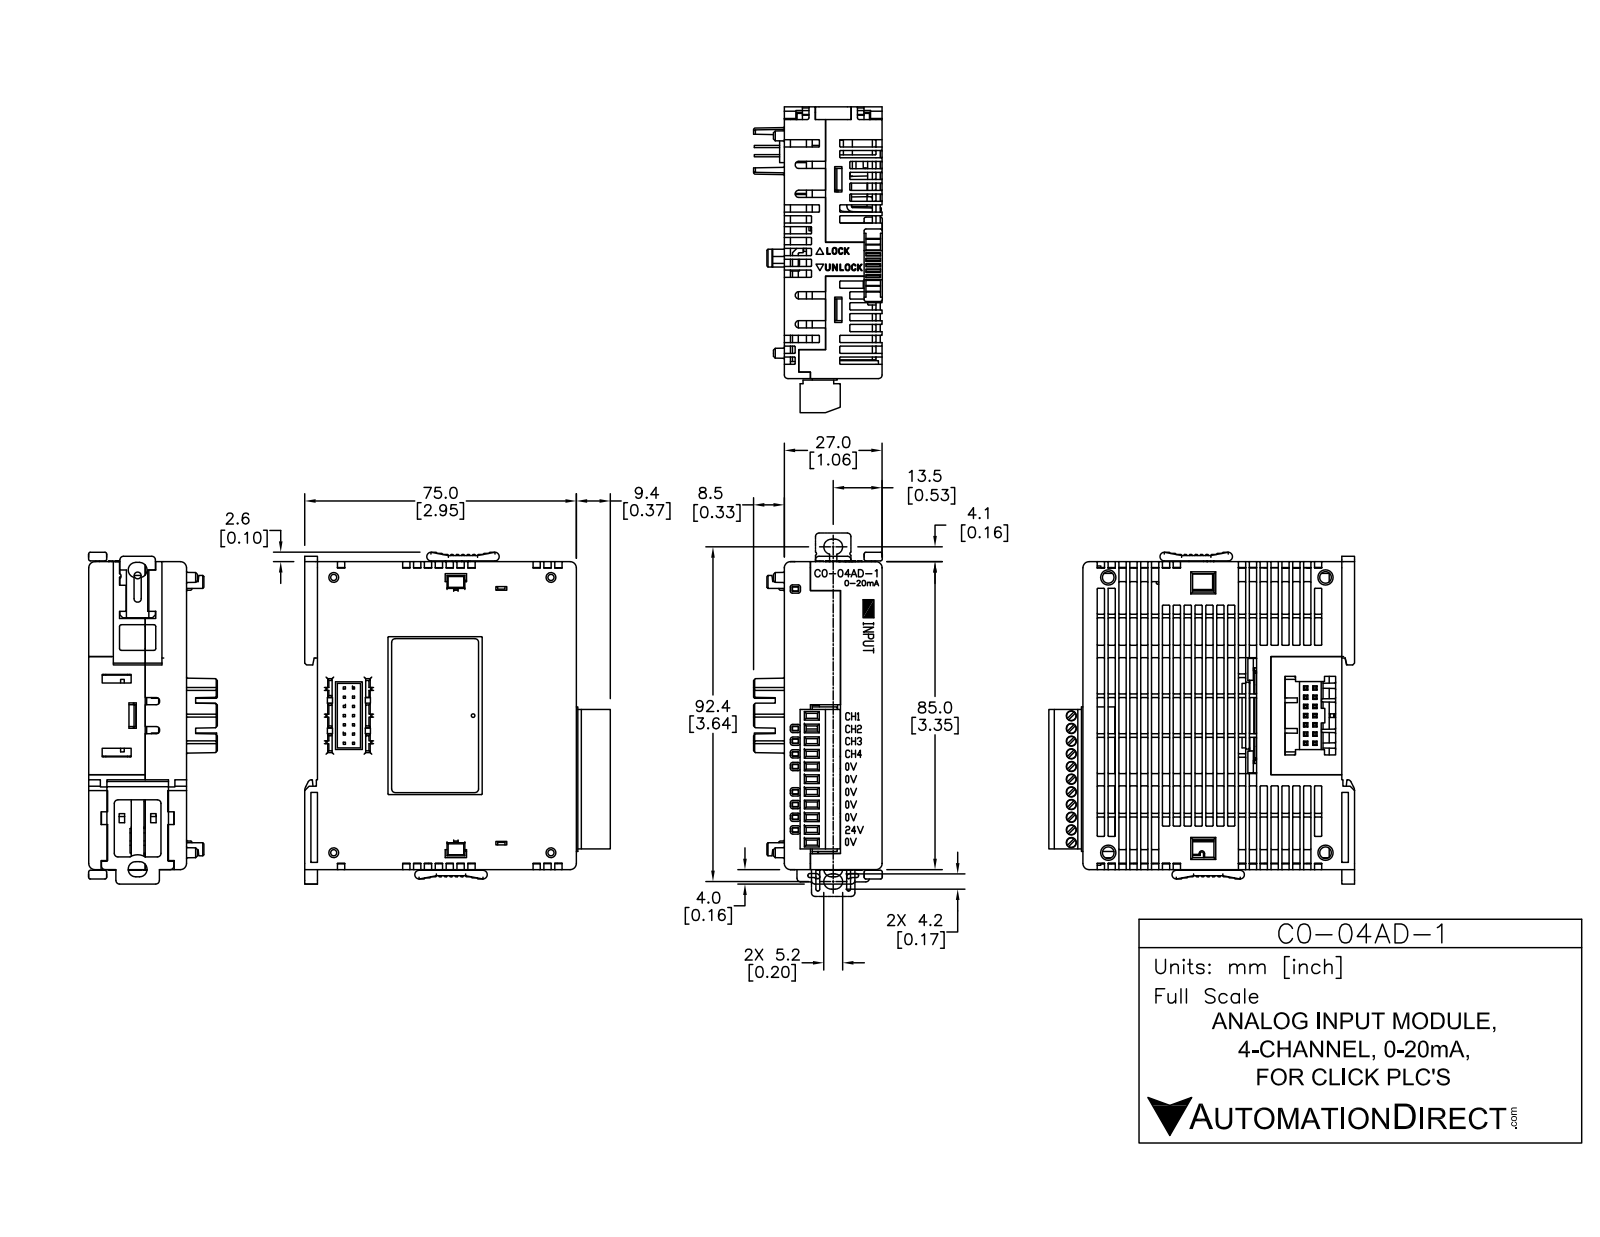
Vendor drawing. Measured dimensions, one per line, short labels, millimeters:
name: C0-04AD-1
written by: SolidWorks 2013 (AUTOMOTIVE_DESIGN)
unit: mm
bodies: 1 solid, 3783 faces (2697 planar, 968 cylindrical, 118 other)
size: 91.6 × 84.4 × 35.55
volume: 162 507 mm³; area: 31 789 mm²
holes: 11× ⌀1, 11× ⌀2.8, 4× ⌀3.2, 2× ⌀2
bosses: 11× ⌀2.6, 1× ⌀1.9
rounds: 570× R0.2, 43× R0.5, 22× R0.3, 18× R1, 12× R1.2, 11× R2.8, 6× R1.7, 4× R2.1
face distances: 27.01, 0.5, 0.51, 26.5, 71.5, 1.7, 85, 26.3, 26.81, 84.5
hole spacings: 3.5, 7, 10.5, 14, 17.5, 21, 24.5, 28
